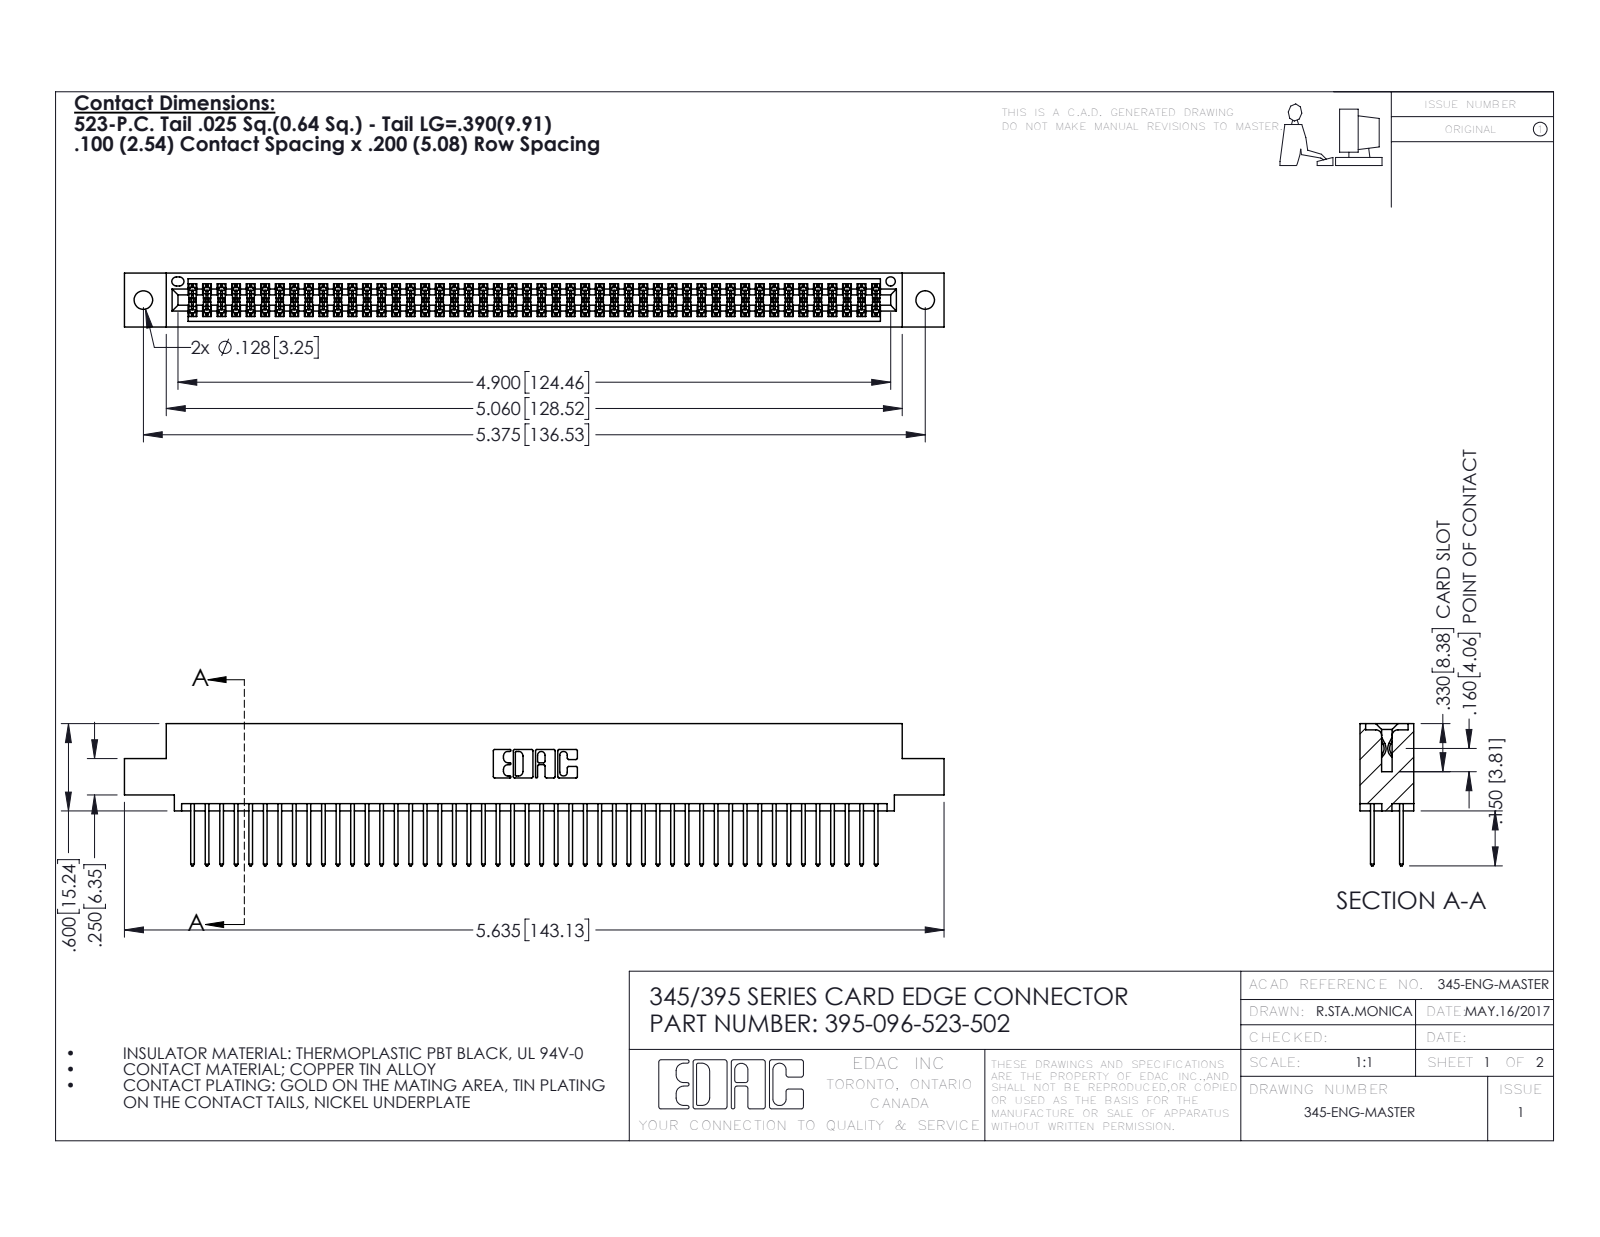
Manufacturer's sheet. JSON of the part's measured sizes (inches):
{"part_name": "345 Part_0.110 Offset - 0.128 Dia; 345-292-001_345-293-123; 395-096-523-502", "step_written_by": "SolidWorks 2016 (CONFIG_CONTROL_DESIGN)", "units": "inches", "bodies": {"solids": 97, "faces": 4930, "planar": 3252, "cylindrical": 1678, "other": 0}, "overall_size": [5.635, 0.977, 0.37], "volume_in3": 0.857, "surface_area_in2": 33.45, "round_holes": [[0.128, 2], [0.064, 1]], "partial_cylinders_radius": [[0.006, 144], [0.01, 96], [0.01, 22], [0.007, 6], [0.031, 6], [0.026, 3], [0.014, 2], [0.019, 2]], "face_to_face_distances": [0.298, 0.072, 0.2, 0.098, 0.272, 0.025, 0.37, 0.225, 0.175, 0.149], "hole_center_spacings": [0.27, 5.139, 5.375]}
